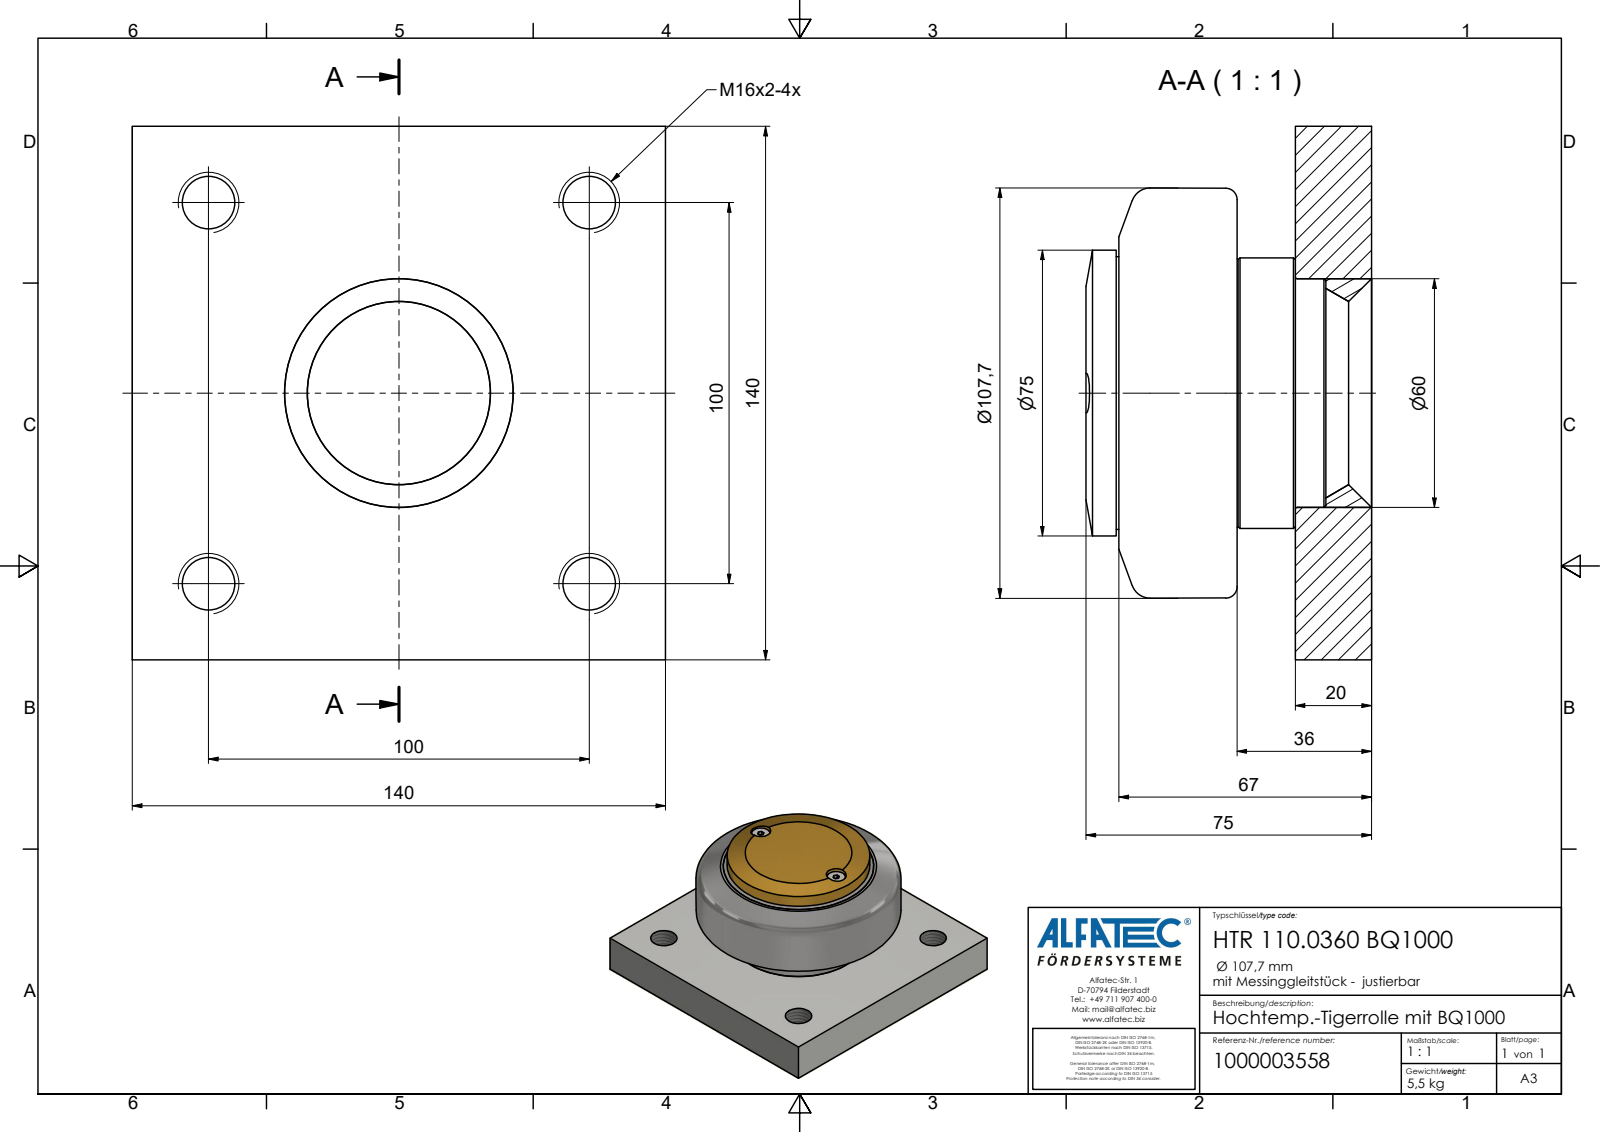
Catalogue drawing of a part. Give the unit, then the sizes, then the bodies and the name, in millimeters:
Units: millimetres
Overall size (bounding box): 140 × 140 × 74.95
Round holes (diameter × count): ⌀13.84 ×4, ⌀10.4 ×2, ⌀3 ×1, ⌀78 ×1, ⌀79 ×1, ⌀83.3 ×1
Round bosses / shafts (diameter × count): ⌀9.75 ×2, ⌀77 ×1, ⌀75 ×1, ⌀71.6 ×1, ⌀71 ×1, ⌀70.5 ×1, ⌀69.3 ×1
Partial cylindrical surfaces — rounded edges, fillets, slot ends (radius × count): R31.5 ×1
Main face-to-face distances: 20, 140, 35.3, 15.3, 74.95, 54.95, 39.65, 6, 29.3, 6.5
Hole centre spacings: 54.63, 70.71, 92.65, 100, 28, 141.42, 56
Volume: 698 982 mm³ · Surface area: 97 125 mm²
Bodies: 1 solid, 71 faces (36 planar, 24 cylindrical, 11 other)
Part name (STEP PRODUCT): HTR 110.0360 BQ1000_Kontur
STEP written by: Autodesk Inventor 2020 (AUTOMOTIVE_DESIGN)
